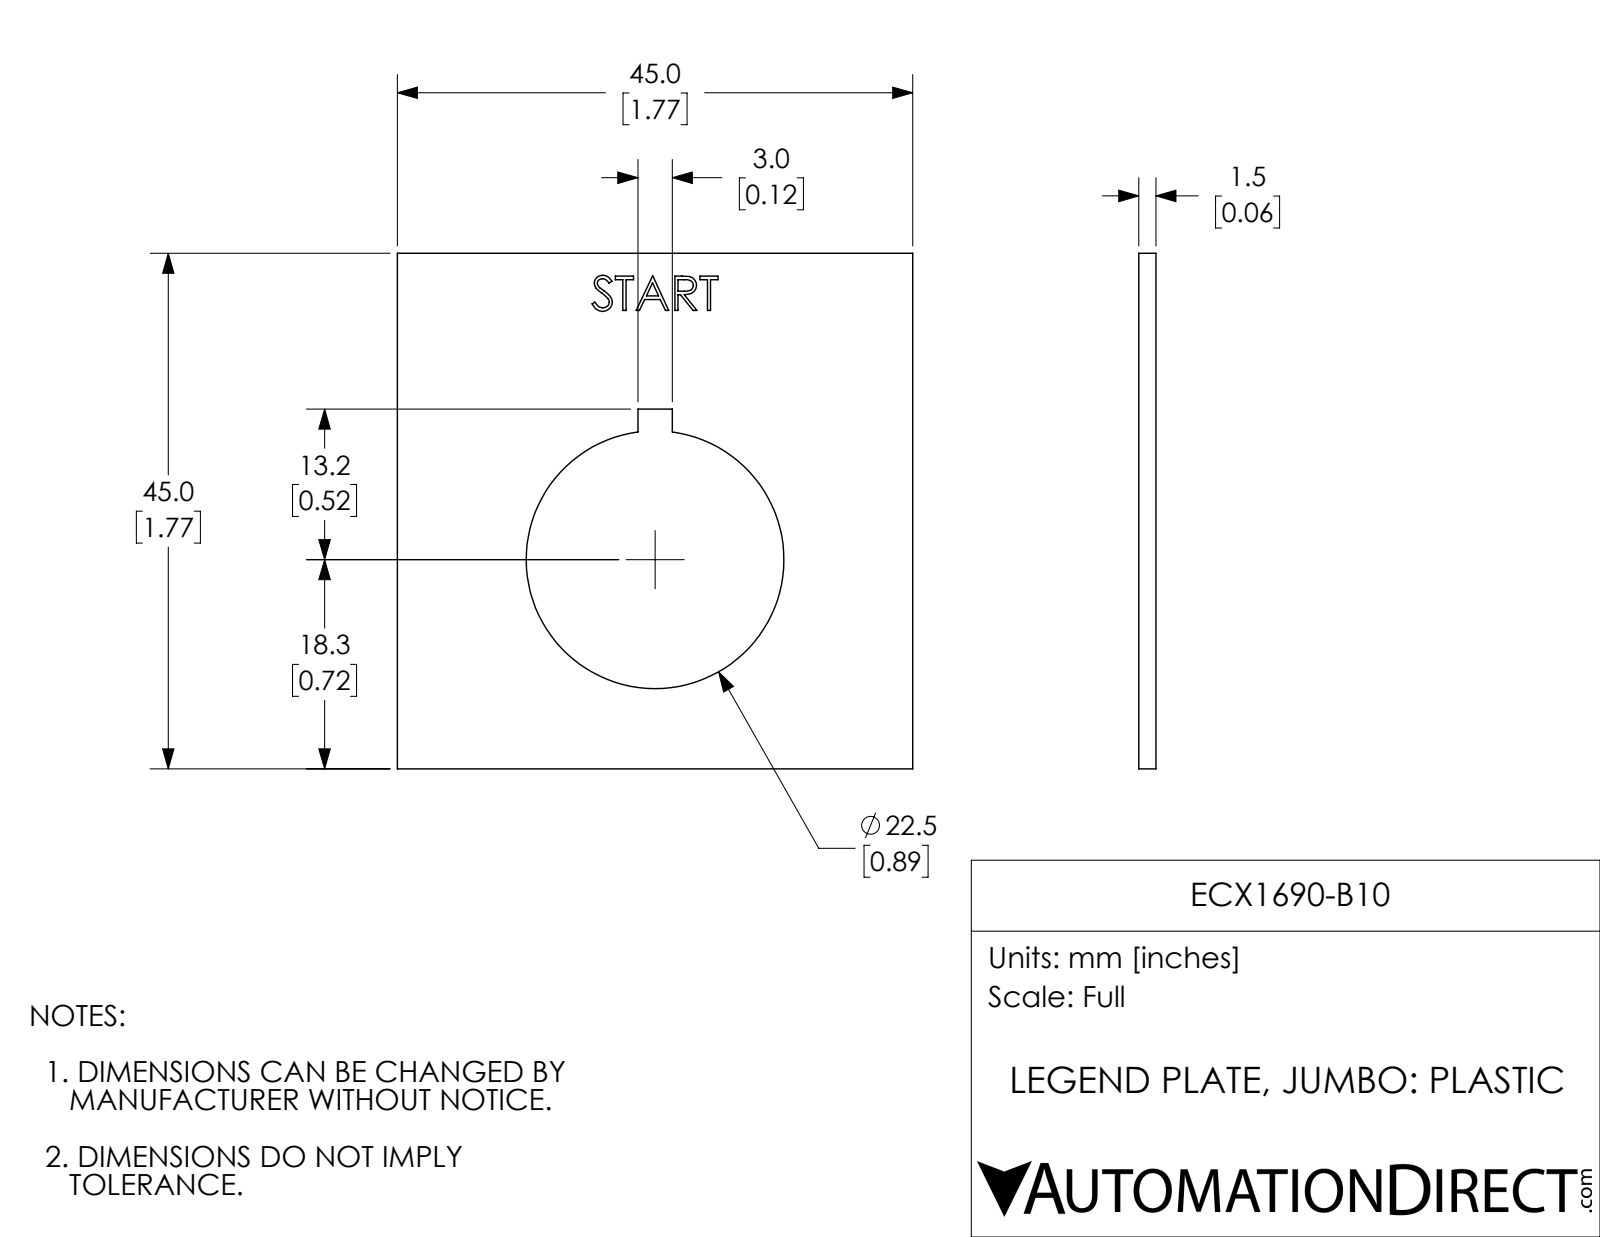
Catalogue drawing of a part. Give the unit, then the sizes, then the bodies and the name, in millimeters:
Units: millimetres
Overall size (bounding box): 45 × 45 × 1.5
Round holes (diameter × count): ⌀22.5 ×1
Main face-to-face distances: 1.5, 45, 1.5, 21, 24, 31.4, 13.6, 3, 7.4, 4.5
Volume: 2 430 mm³ · Surface area: 3 627 mm²
Bodies: 1 solid, 79 faces (56 planar, 3 cylindrical, 20 other)
Part name (STEP PRODUCT): ECX1690-B10
STEP written by: SolidWorks 2018 (AUTOMOTIVE_DESIGN)
